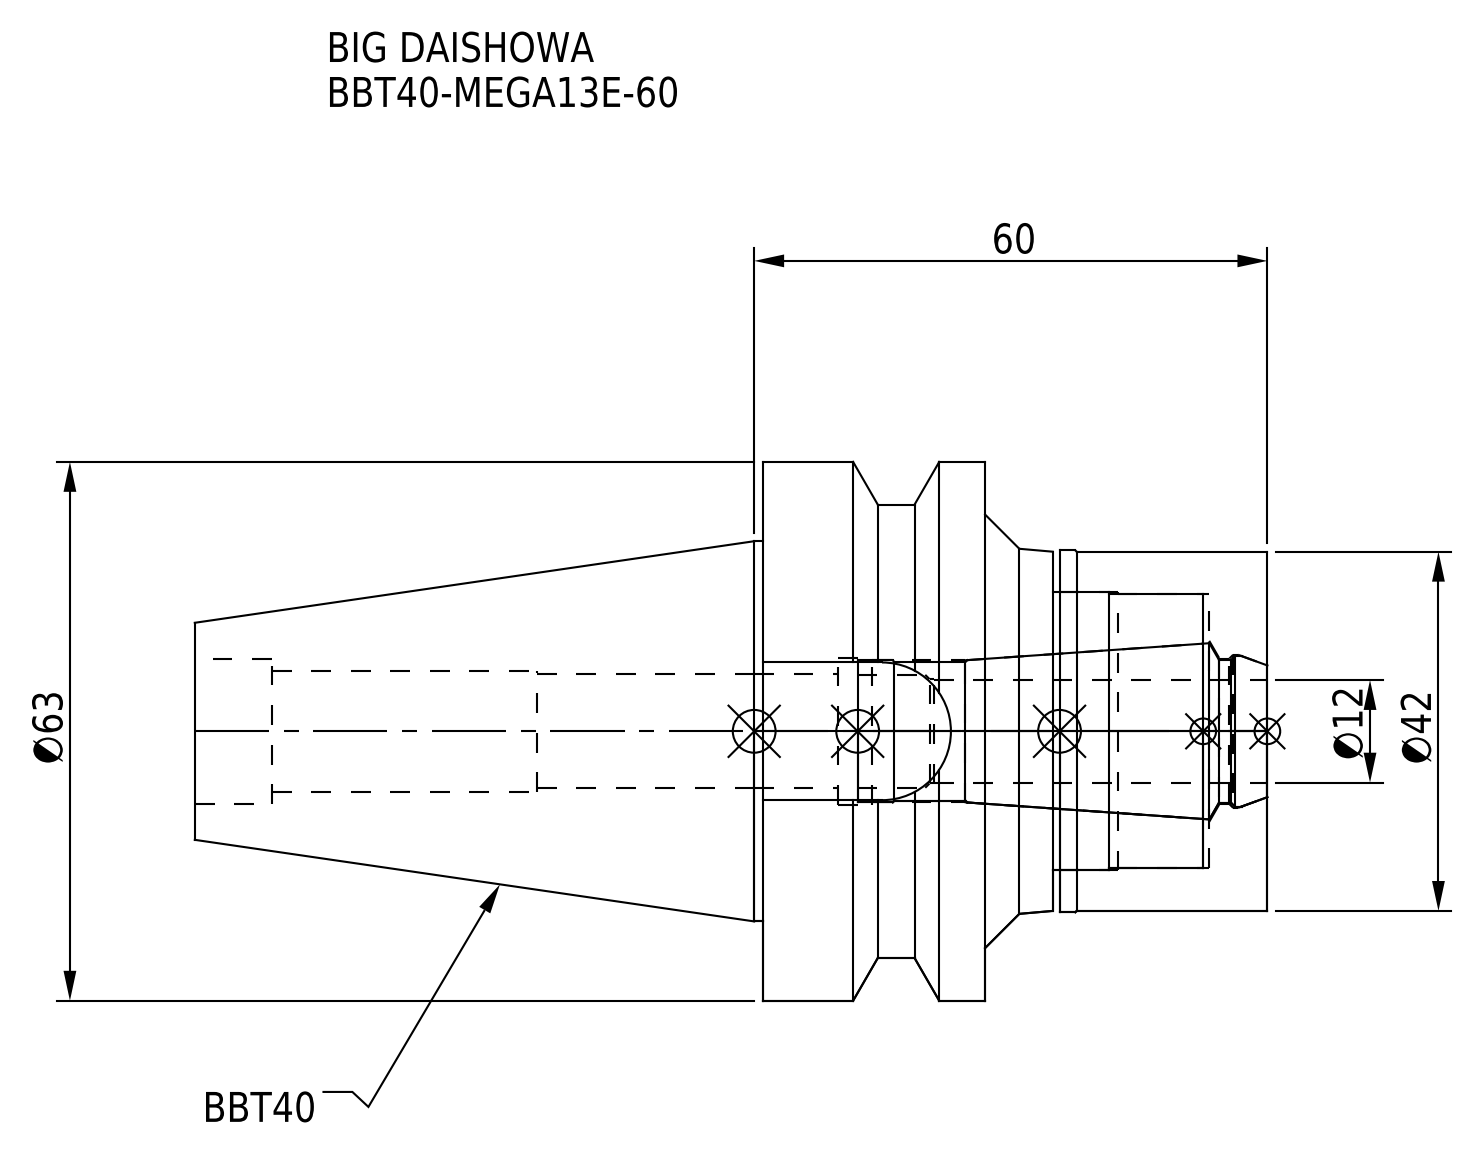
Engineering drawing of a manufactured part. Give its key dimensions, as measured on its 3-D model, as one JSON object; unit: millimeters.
{"part_name": "BBT40-MEGA13E-60_1.stp; BBT40ME13060-120_ASM.stp; BBT40-MEGA13E-60; MEN13_1.stp (+3 more)", "step_written_by": "SolidWorks 2019 (CONFIG_CONTROL_DESIGN)", "units": "millimeters", "bodies": {"solids": 2, "faces": 78, "planar": 20, "cylindrical": 38, "other": 20}, "overall_size": [125.4, 63, 63], "volume_mm3": 157433, "surface_area_mm2": 34396, "round_holes": [[13.3, 1], [14.2, 1], [16.6, 1], [17, 1], [17.2, 1], [17.9, 1], [32, 1], [32.5, 1]], "round_bosses_or_shafts": [[63, 1], [53, 1], [44.45, 1], [42.3, 1], [42, 1]], "partial_cylinders_radius": [[8.05, 1]], "face_to_face_distances": [59, 33, 26, 25.1, 24.3, 8.7, 34.7, 0.8, 7.9, 33.9]}
